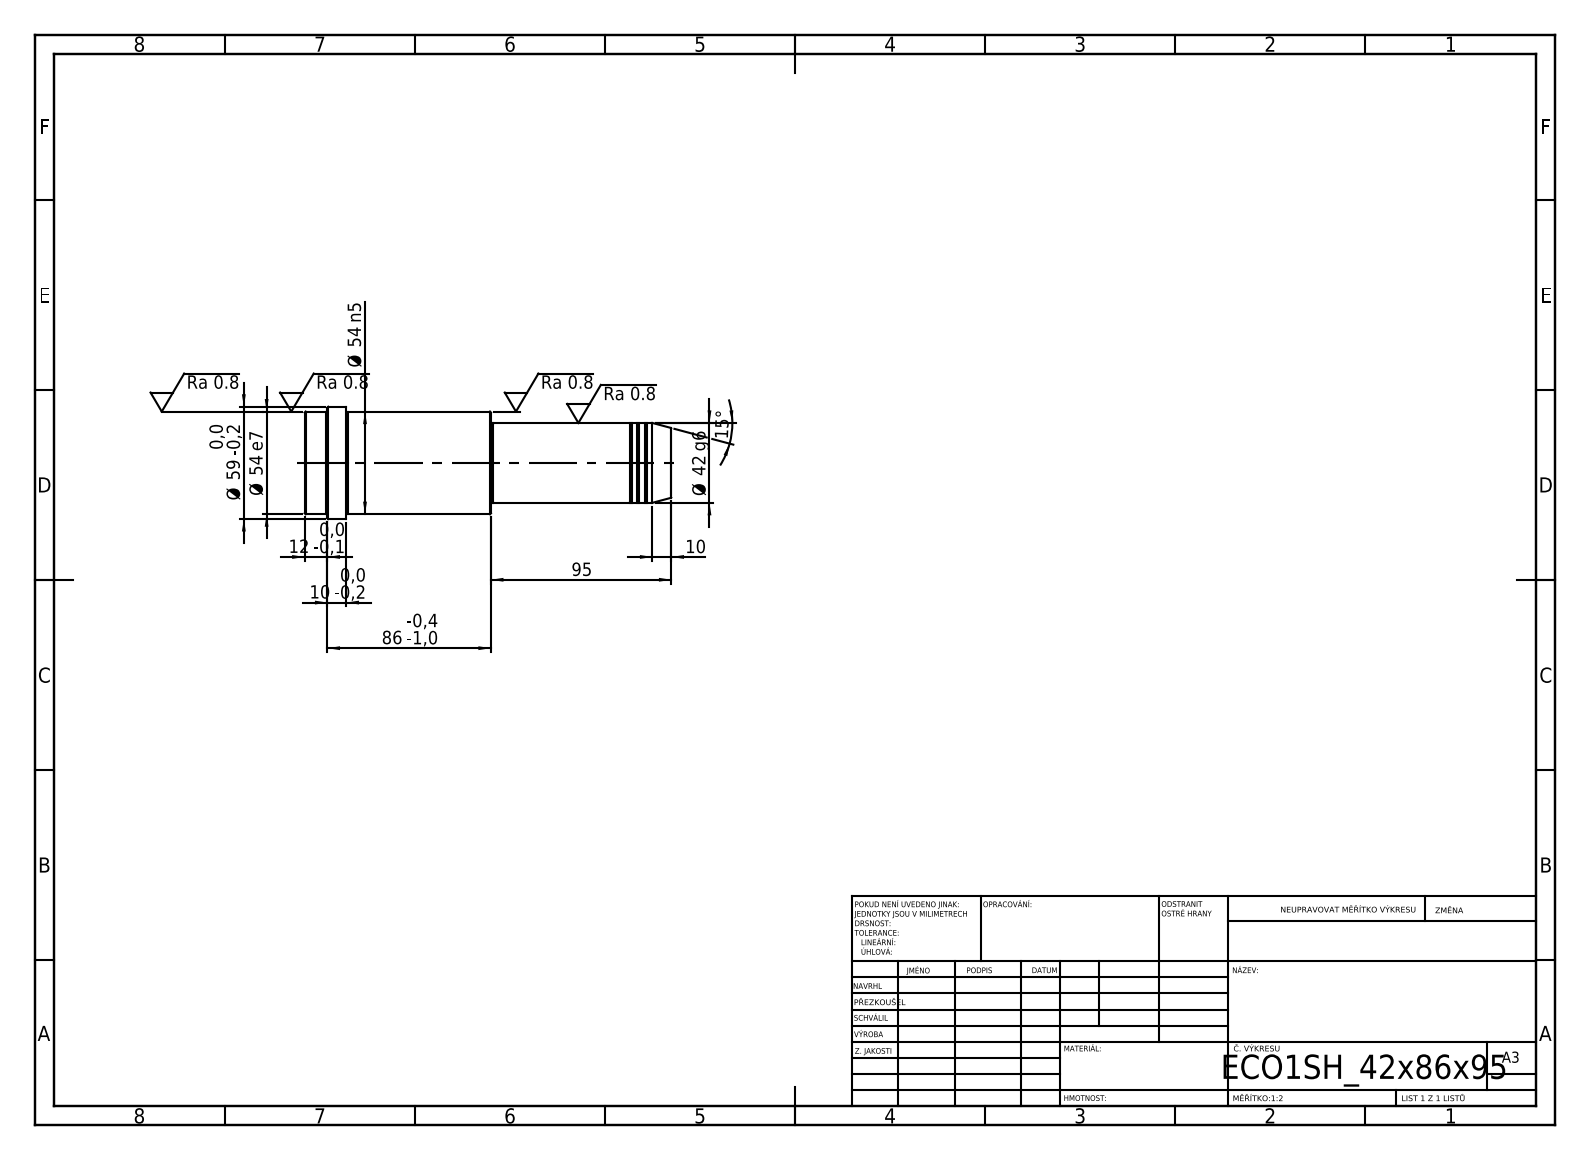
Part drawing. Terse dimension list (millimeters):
written by: SolidWorks 2019 (CONFIG_CONTROL_DESIGN)
unit: mm
bodies: 1 solid, 52 faces (6 planar, 16 cylindrical, 30 other)
size: 193 × 59 × 59
volume: 358 384 mm³; area: 34 777 mm²
bosses: 1× ⌀59, 1× ⌀54, 1× ⌀42, 1× ⌀41
face distances: 193, 95, 98, 171, 76, 22, 181, 86, 10, 12
